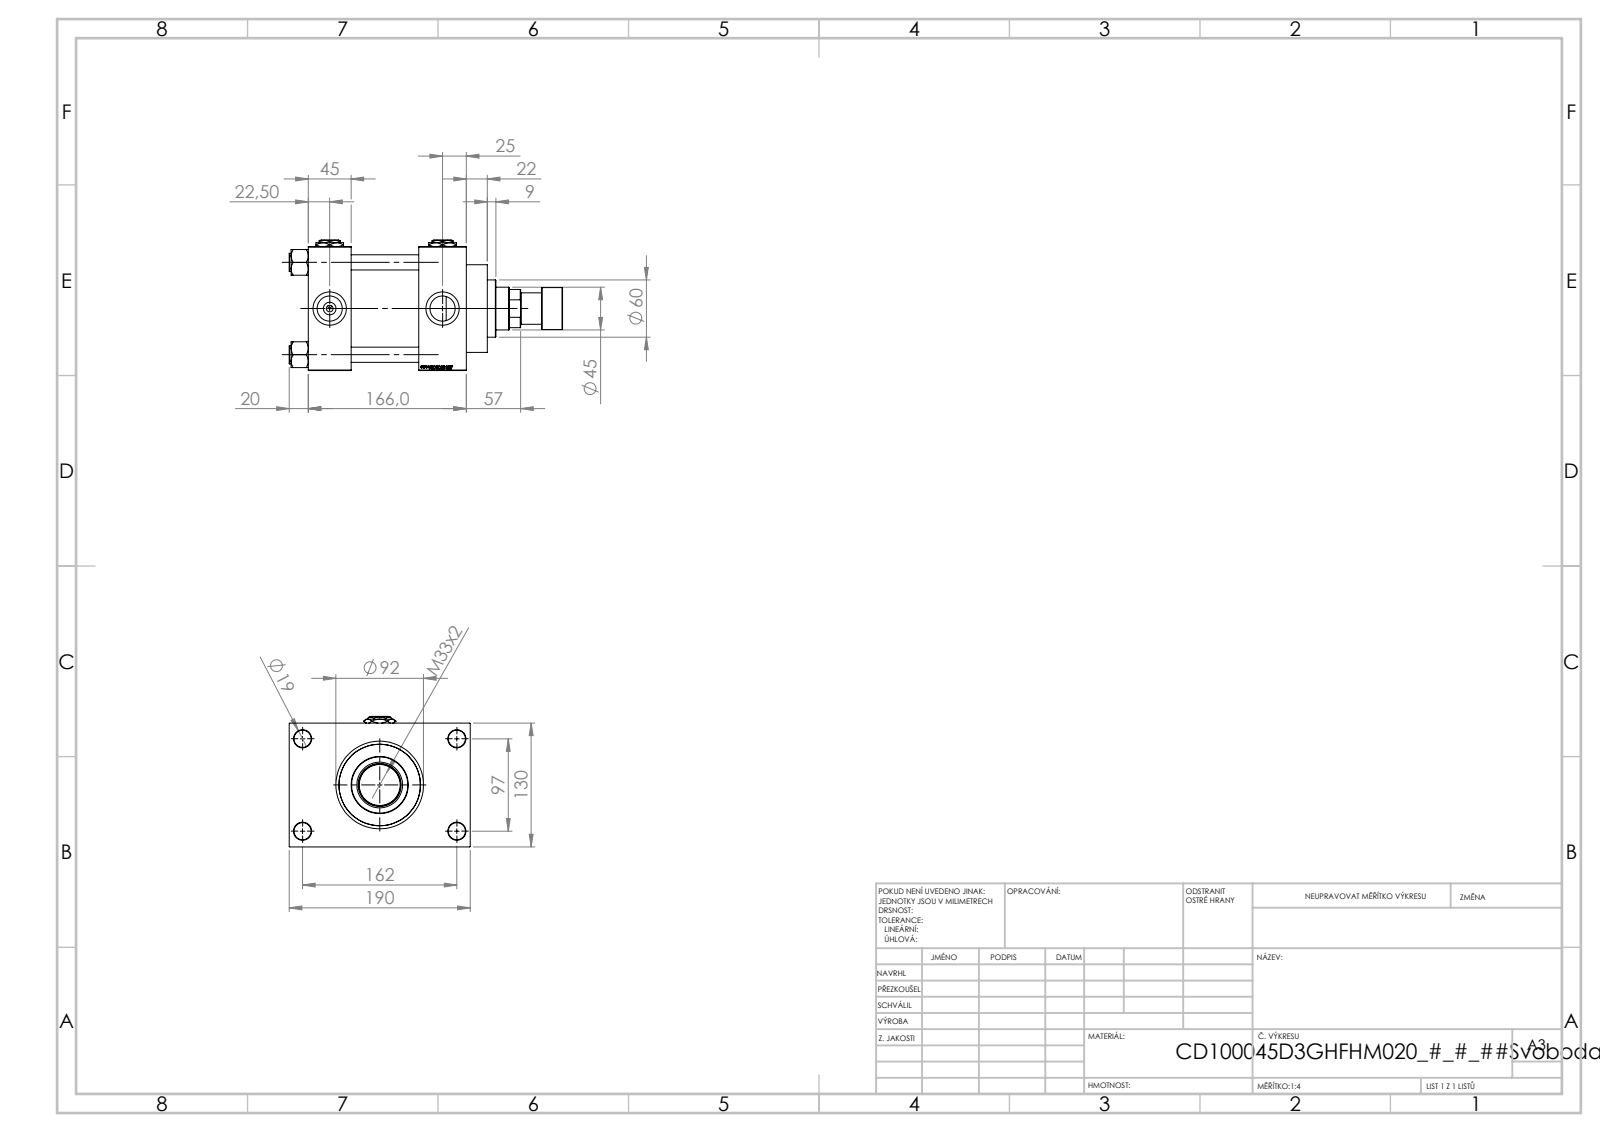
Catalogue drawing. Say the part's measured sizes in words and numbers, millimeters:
The part is named "V215CD_VC_A; V215CR_ROD_END_F; V215CD_NUT_M5_D; Zatka_pro_OIL_PORT (+3 more)". Its 3-D file was written by "SolidWorks 2019 (CONFIG_CONTROL_DESIGN)". It is 14 solids with 1265 faces: 596 planar, 103 cylindrical and 566 other. Overall it measures 287 by 190 by 137 millimeters. Its volume is 2 628 000 cubic millimeters and its surface area 370 174 square millimeters. Round holes: 4 of diameter 16, 4 of diameter 18, 4 of diameter 26.44, 4 of diameter 35, 3 of diameter 7, 1 of diameter 31.5, 1 of diameter 45, 1 of diameter 48, 1 of diameter 76, 1 of diameter 85.5, 1 of diameter 100. Round bosses or shafts: 4 of diameter 19, 1 of diameter 106, 1 of diameter 92, 1 of diameter 60, 1 of diameter 44, 1 of diameter 33. The main face-to-face distances are 116, 45, 130, 71, 166, 121, 50, 30, 160, 70. The hole center spacings are 32.55, 68.52, 94.41, 96.9, 102.27, 129.45, 161.73, 97.
